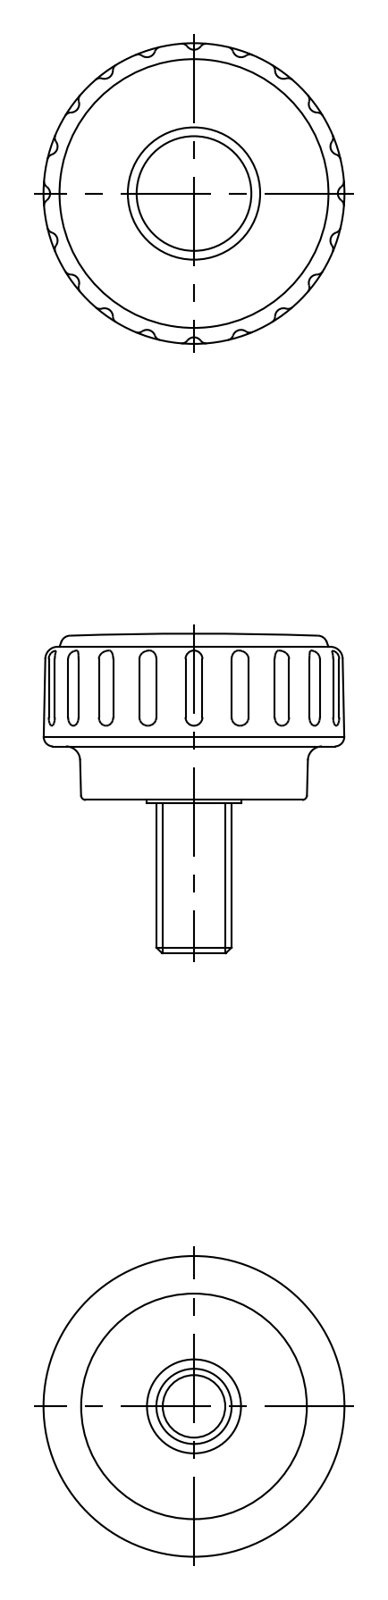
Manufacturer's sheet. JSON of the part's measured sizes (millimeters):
{"part_name": "screw; knob; KDMS_32_M8_16_WH_24079_36", "step_written_by": "CADfix (AUTOMOTIVE_DESIGN)", "units": "millimeters", "bodies": {"solids": 2, "faces": 69, "planar": 0, "cylindrical": 0, "other": 69}, "overall_size": [33.94, 32.03, 31.96], "volume_mm3": 12309, "surface_area_mm2": 4132}
